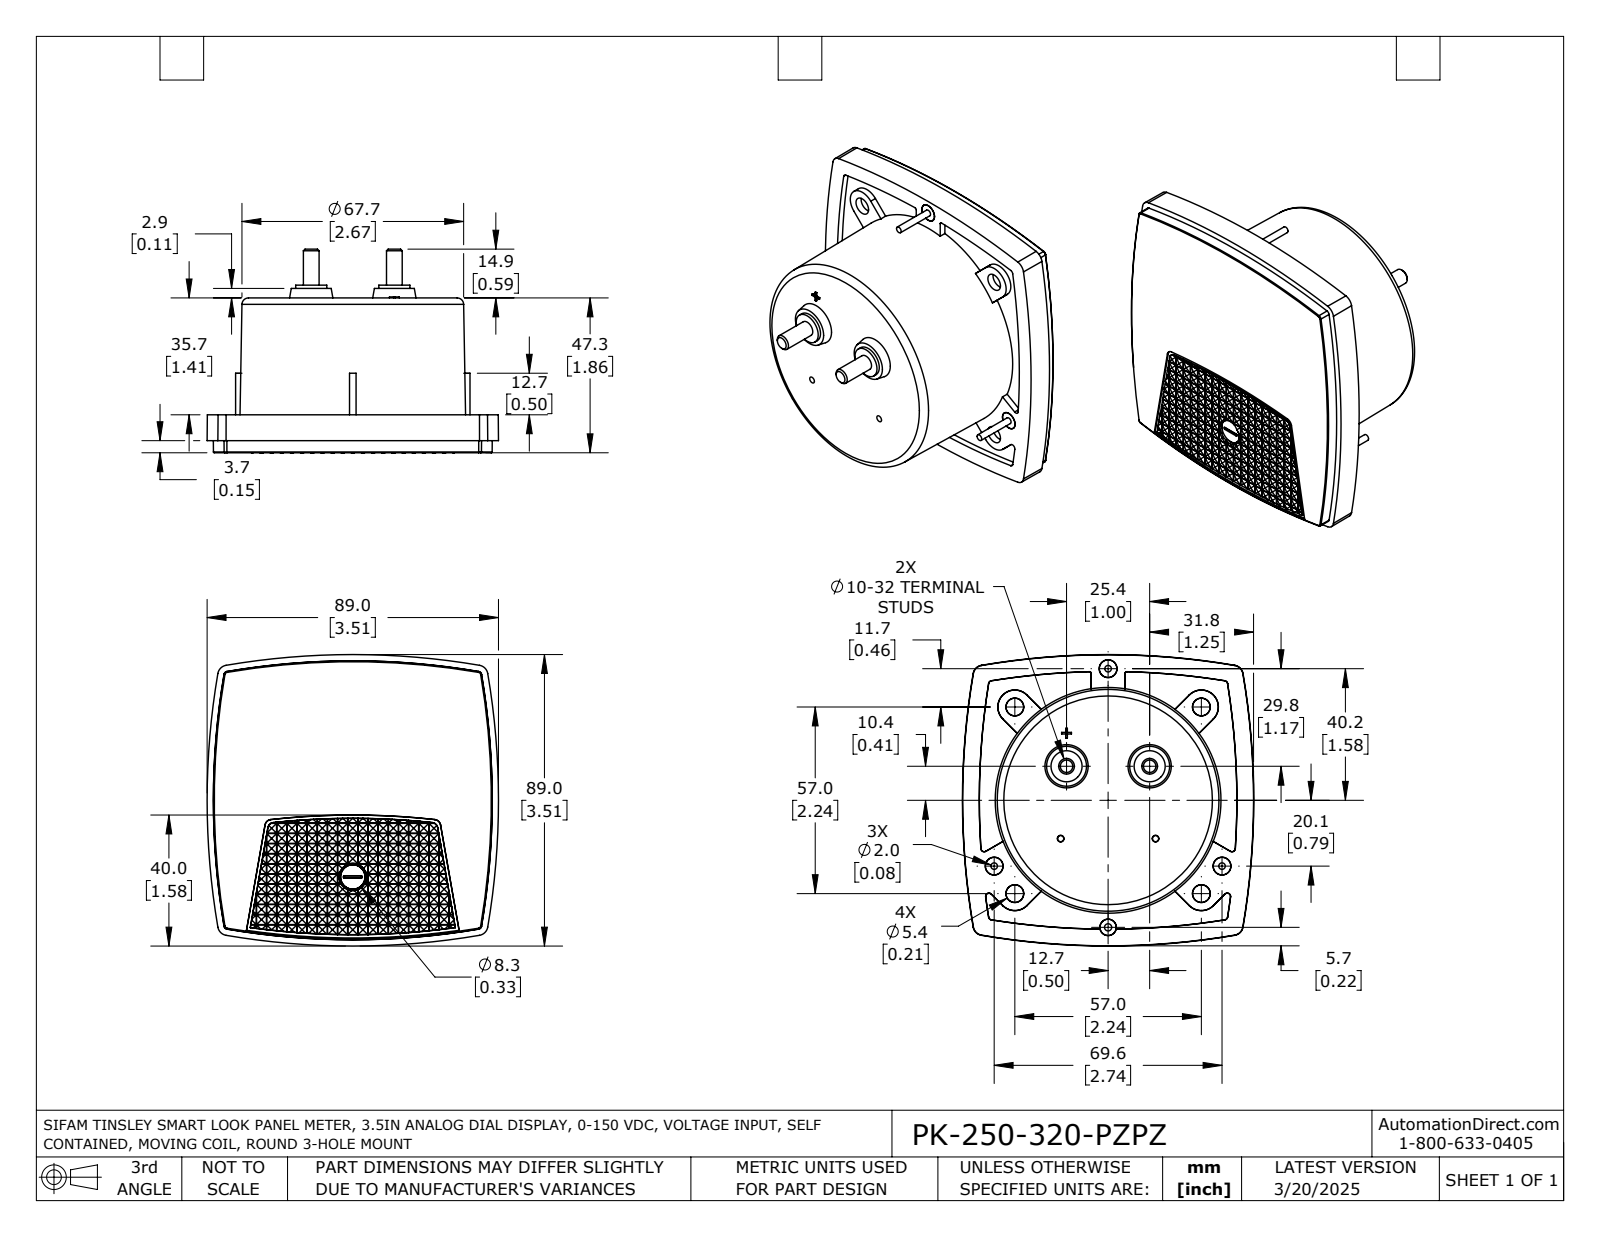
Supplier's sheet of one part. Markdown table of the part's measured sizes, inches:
| quantity | value |
| --- | --- |
| part name | PK-250-320-PZPZ |
| STEP written by | SolidWorks 2021 (AUTOMOTIVE_DESIGN) |
| units | inches |
| bodies | 1 solid, 1078 faces (950 planar, 23 cylindrical, 105 other) |
| overall size | 3.505 × 3.505 × 2.453 |
| volume | 12.99 in³ |
| surface area | 44.29 in² |
| round holes (diameter × count) | 0.087 × 1 |
| round bosses / shafts (diameter × count) | 0.213 × 3, 0.079 × 3, 0.374 × 2, 0.189 × 2 |
| partial cylindrical surfaces (radius × count) | 8.961 × 1 |
| main face-to-face distances | 1.862, 1.406, 0.457, 0.079, 1.484, 0.378, 0.024, 0.096, 0.072, 0.12 |
